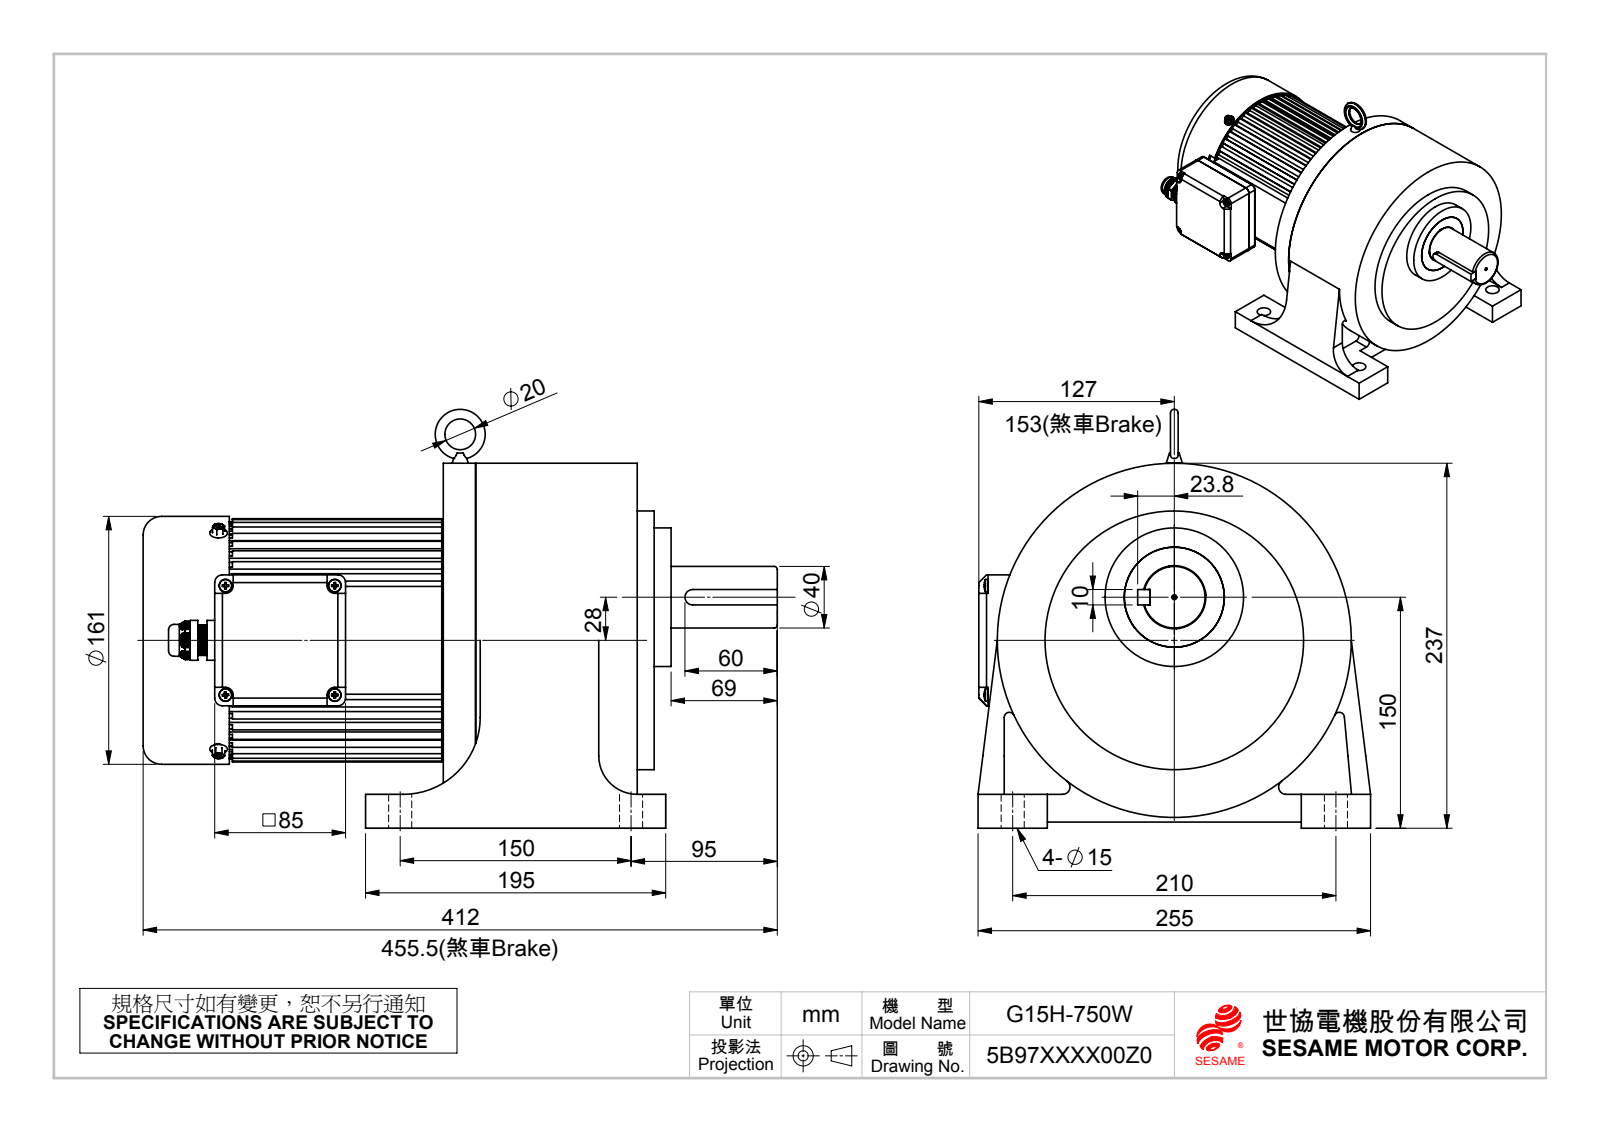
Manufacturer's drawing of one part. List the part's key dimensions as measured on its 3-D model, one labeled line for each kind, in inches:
Part name (STEP PRODUCT): 出線盒墊片JTH-UP3(PVC2mm厚); 10x8xL_60L; 750W風扇蓋159＊56; 750後蓋-M-SAB-45_3.烤車鑽 (+8 more)
STEP written by: SolidWorks 2010 (CONFIG_CONTROL_DESIGN)
Units: inches
Bodies: 20 solids, 2837 faces (951 planar, 856 cylindrical, 1030 other)
Overall size (bounding box): 16.22 × 10.709 × 10.039
Volume: 615.7 in³ · Surface area: 1 119 in²
Round holes (diameter × count): ⌀0.197 ×11, ⌀0.13 ×9, ⌀0.315 ×5, ⌀0.236 ×4, ⌀0.591 ×4, ⌀0.165 ×3, ⌀0.079 ×1, ⌀0.268 ×1, ⌀0.425 ×1, ⌀0.65 ×1, ⌀0.787 ×1, ⌀1.614 ×1
Round bosses / shafts (diameter × count): ⌀0.327 ×4, ⌀0.157 ×4, ⌀0.197 ×3, ⌀9.055 ×1, ⌀8.583 ×1, ⌀6.614 ×1, ⌀6.339 ×1, ⌀6.26 ×1
Partial cylindrical surfaces — rounded edges, fillets, slot ends (radius × count): R0.079 ×46, R0.039 ×36, R0.197 ×10, R0.02 ×6, R0.098 ×6, R0.1 ×4, R0.14 ×4, R0.13 ×2
Main face-to-face distances: 0.197, 0.866, 1.063, 0.039, 7.638, 0.157, 0.827, 1.024, 0.709, 5.551
Hole centre spacings: 1.772, 2.55, 2.795, 0.433, 0.453, 0.575, 0.582, 0.683
